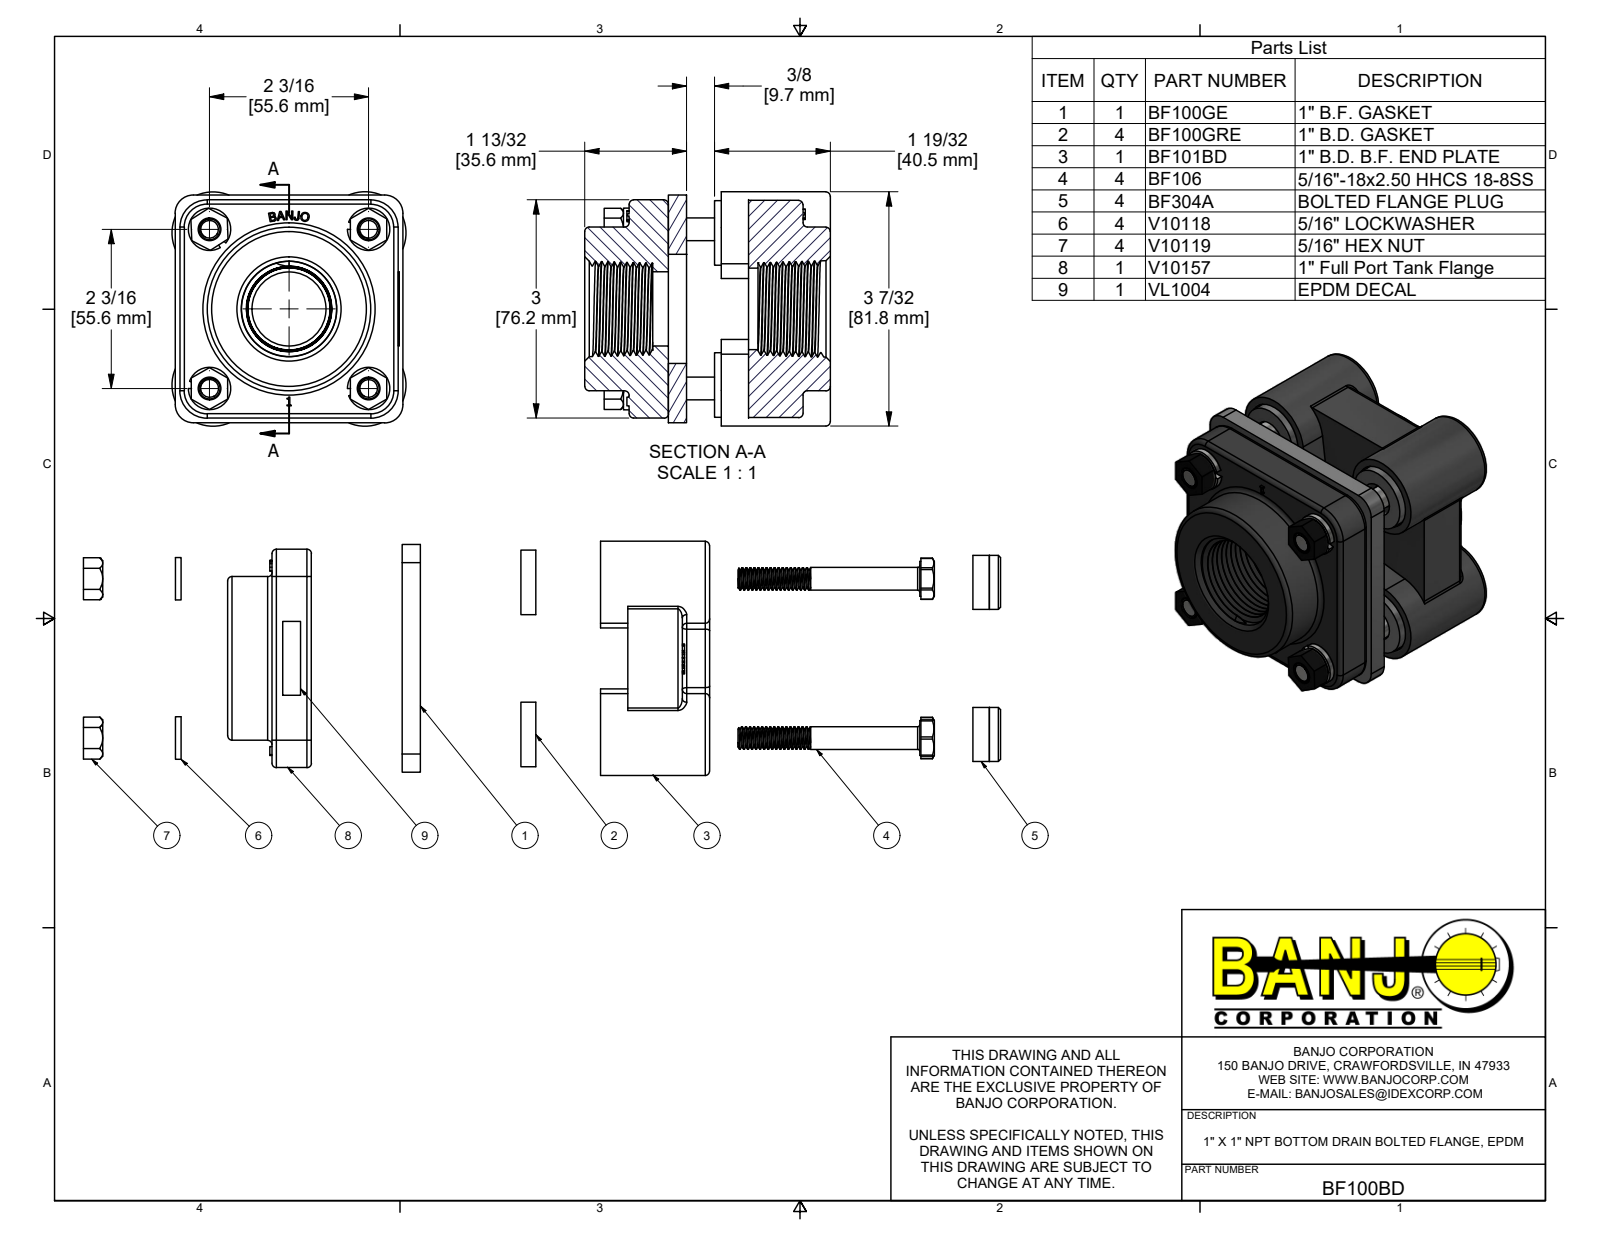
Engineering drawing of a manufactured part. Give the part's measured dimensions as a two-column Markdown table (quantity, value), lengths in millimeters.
| quantity | value |
| --- | --- |
| part name | BF100BD; BF101BD; BF106; BF304A (+6 more) |
| STEP written by | Autodesk Inventor 2019 (AUTOMOTIVE_DESIGN) |
| units | millimeters |
| bodies | 24 solids, 1232 faces (512 planar, 360 cylindrical, 360 other) |
| overall size | 534.4 × 81.8 × 81.8 |
| volume | 301 700 mm³ |
| surface area | 146 800 mm² |
| round holes (diameter × count) | 6.4 × 4, 8 × 4, 8.2 × 4, 8.6 × 4, 8.7 × 4, 8.9 × 4, 12.2 × 4, 18.1 × 4, 19.1 × 4, 23.4 × 4, 25.9 × 1, 28.4 × 1 |
| round bosses / shafts (diameter × count) | 22.5 × 4, 18.8 × 4, 14.8 × 4, 12.7 × 4, 12.2 × 4, 7.7 × 4, 6.2 × 4, 57.2 × 1 |
| partial cylindrical surfaces (radius × count) | 1.5 × 28, 0.8 × 24, 6.4 × 4, 9.5 × 4, 14.4 × 4, 10 × 1, 10 × 1, 13.1 × 1 |
| main face-to-face distances | 6.4, 50.2, 56.5, 6.7, 13.7, 20.1, 70.3, 21.6, 41.7, 28 |
| hole center spacings | 54.3, 54.5, 55.7, 1.8, 2, 37.5, 39.3, 39.5 |
